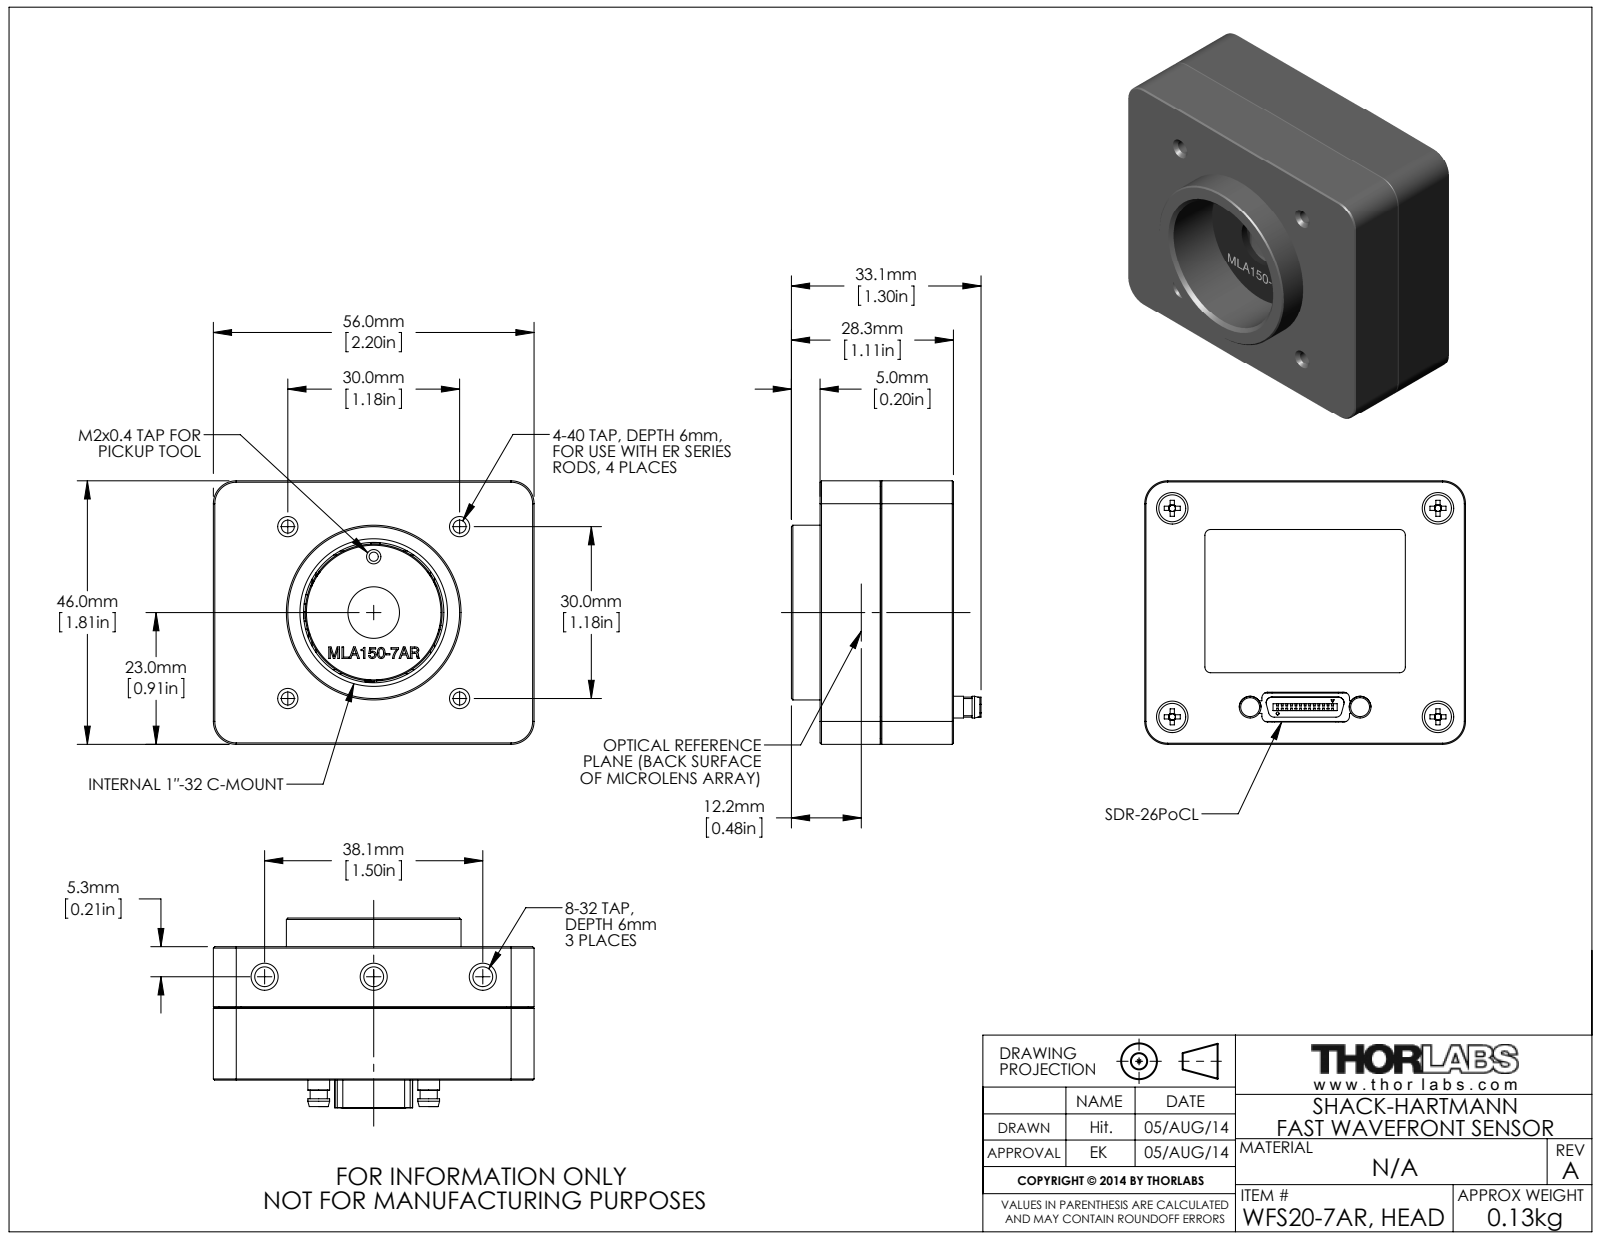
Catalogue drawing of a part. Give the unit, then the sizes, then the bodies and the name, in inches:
Units: inches
Overall size (bounding box): 2.205 × 1.811 × 1.304
Round holes (diameter × count): ⌀0.024 ×26, ⌀0.126 ×6, ⌀0.081 ×4, ⌀0.089 ×4, ⌀0.106 ×4, ⌀0.114 ×4, ⌀0.118 ×4, ⌀0.236 ×4, ⌀0.075 ×3, ⌀0.136 ×3, ⌀0.047 ×2, ⌀0.069 ×2
Round bosses / shafts (diameter × count): ⌀0.028 ×108, ⌀0.039 ×11, ⌀0.118 ×8, ⌀0.22 ×4, ⌀0.185 ×4, ⌀0.098 ×4, ⌀0.083 ×4, ⌀0.15 ×2
Partial cylindrical surfaces — rounded edges, fillets, slot ends (radius × count): R0.039 ×19, R0.079 ×12, R0.007 ×6, R0.008 ×4, R0.108 ×4, R0.122 ×4, R0.138 ×4, R0.15 ×4
Main face-to-face distances: 0.59, 0.653, 0.063, 0.138, 0.763, 0.154, 0.531, 0.058, 0.122, 0.039
Hole centre spacings: 0.055, 0.063, 0.105, 0.225, 0.126, 0.138, 0.164, 0.176
Volume: 4.368 in³ · Surface area: 68.6 in²
Bodies: 51 solids, 2428 faces (1164 planar, 687 cylindrical, 577 other)
Part name (STEP PRODUCT): Halter Teil2 Baugruppe; MTN003816; Linsenarray; Halter Teil3 Typ150-7AR_mit Laserbeschriftung (+8 more)
STEP written by: SolidWorks 2014 (AUTOMOTIVE_DESIGN)
